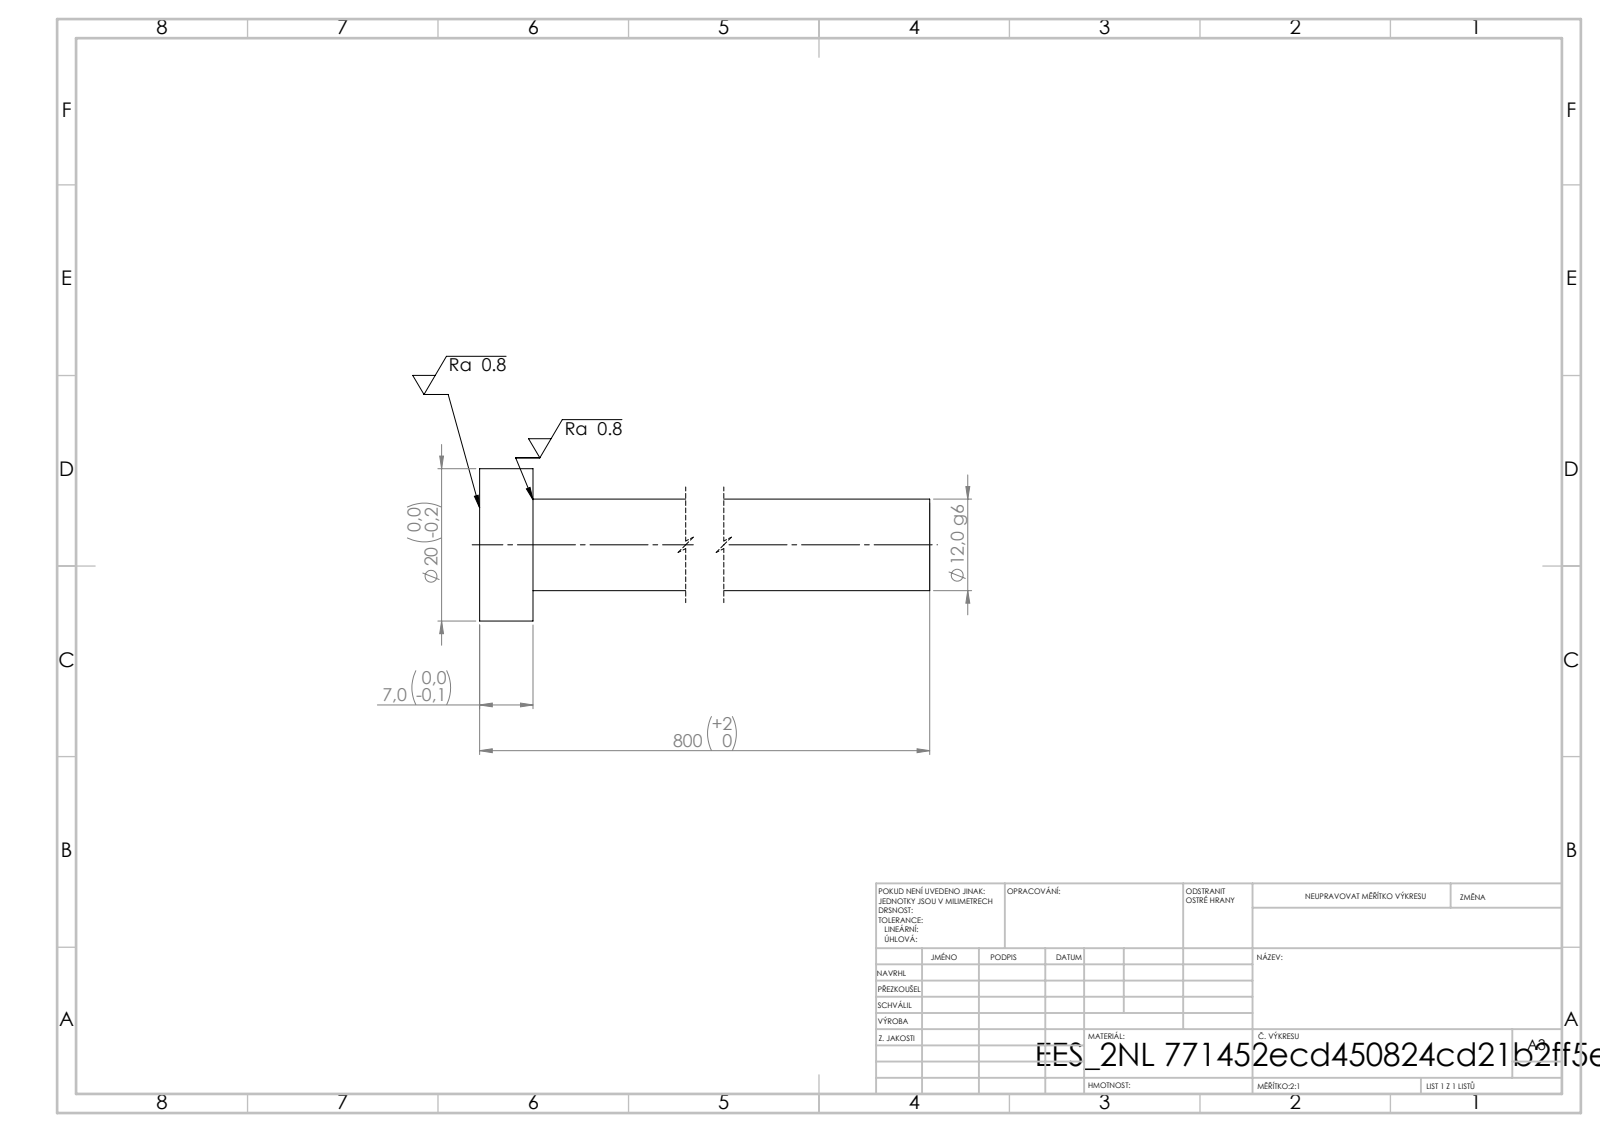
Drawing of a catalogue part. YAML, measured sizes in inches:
step_written_by: "SolidWorks 2019 (CONFIG_CONTROL_DESIGN)"
units: inches
bodies: {solids: 1, faces: 7, planar: 3, cylindrical: 4, other: 0}
overall_size: [31.496, 0.787, 0.787]
volume: 5.607
surface_area: 47.99
round_bosses_or_shafts:
  - {diameter: 0.787, count: 1}
  - {diameter: 0.472, count: 1}
face_to_face_distances: [0.276, 31.496, 31.22]
